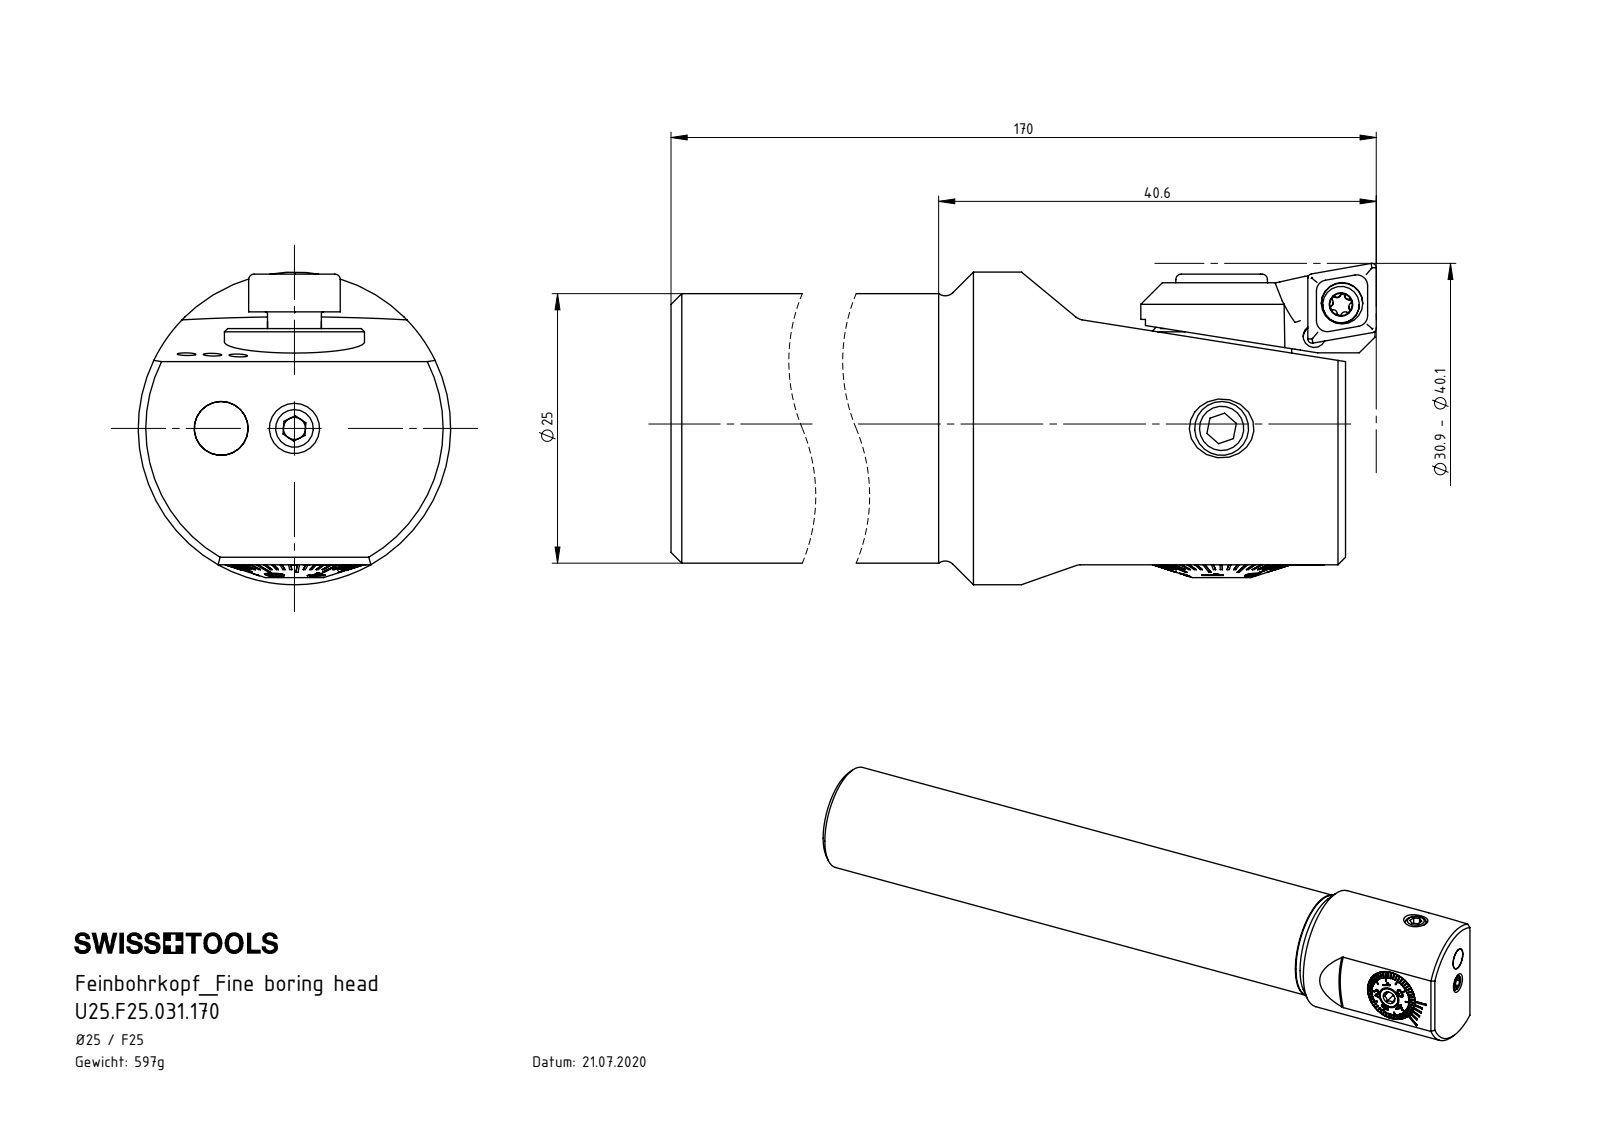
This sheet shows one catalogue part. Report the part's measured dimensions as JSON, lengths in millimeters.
{"part_name": "Fxx-MAB.xxx.xxx_A_F25-DA3; U25.F25.AA4.170; F25-BG2.008.009_A; F25-BG2.010.011_A (+8 more)", "step_written_by": "SolidWorks 2017 (AUTOMOTIVE_DESIGN)", "units": "millimeters", "bodies": {"solids": 14, "faces": 528, "planar": 310, "cylindrical": 59, "other": 159}, "overall_size": [167.15, 29, 29], "volume_mm3": 76374, "surface_area_mm2": 23787, "round_holes": [[1.5, 3], [2.5, 2], [4.2, 2], [2.05, 1], [2.4, 1], [2.7, 1], [3, 1], [3.3, 1], [5, 1], [5.5, 1], [6.4, 1], [7.3, 1]], "round_bosses_or_shafts": [[5, 2], [4.95, 2], [29, 1], [25, 1], [13, 1], [12.98, 1], [12.85, 1], [10.65, 1]], "partial_cylinders_radius": [[1.4, 4], [0.5, 2], [1.5, 2], [0.2, 1], [1.25, 1], [2, 1]], "face_to_face_distances": [167.15, 1.5, 3.91, 0.81, 3.1, 1.6, 2.31, 18, 19.6, 21.1], "hole_center_spacings": [6.8, 7.32]}
